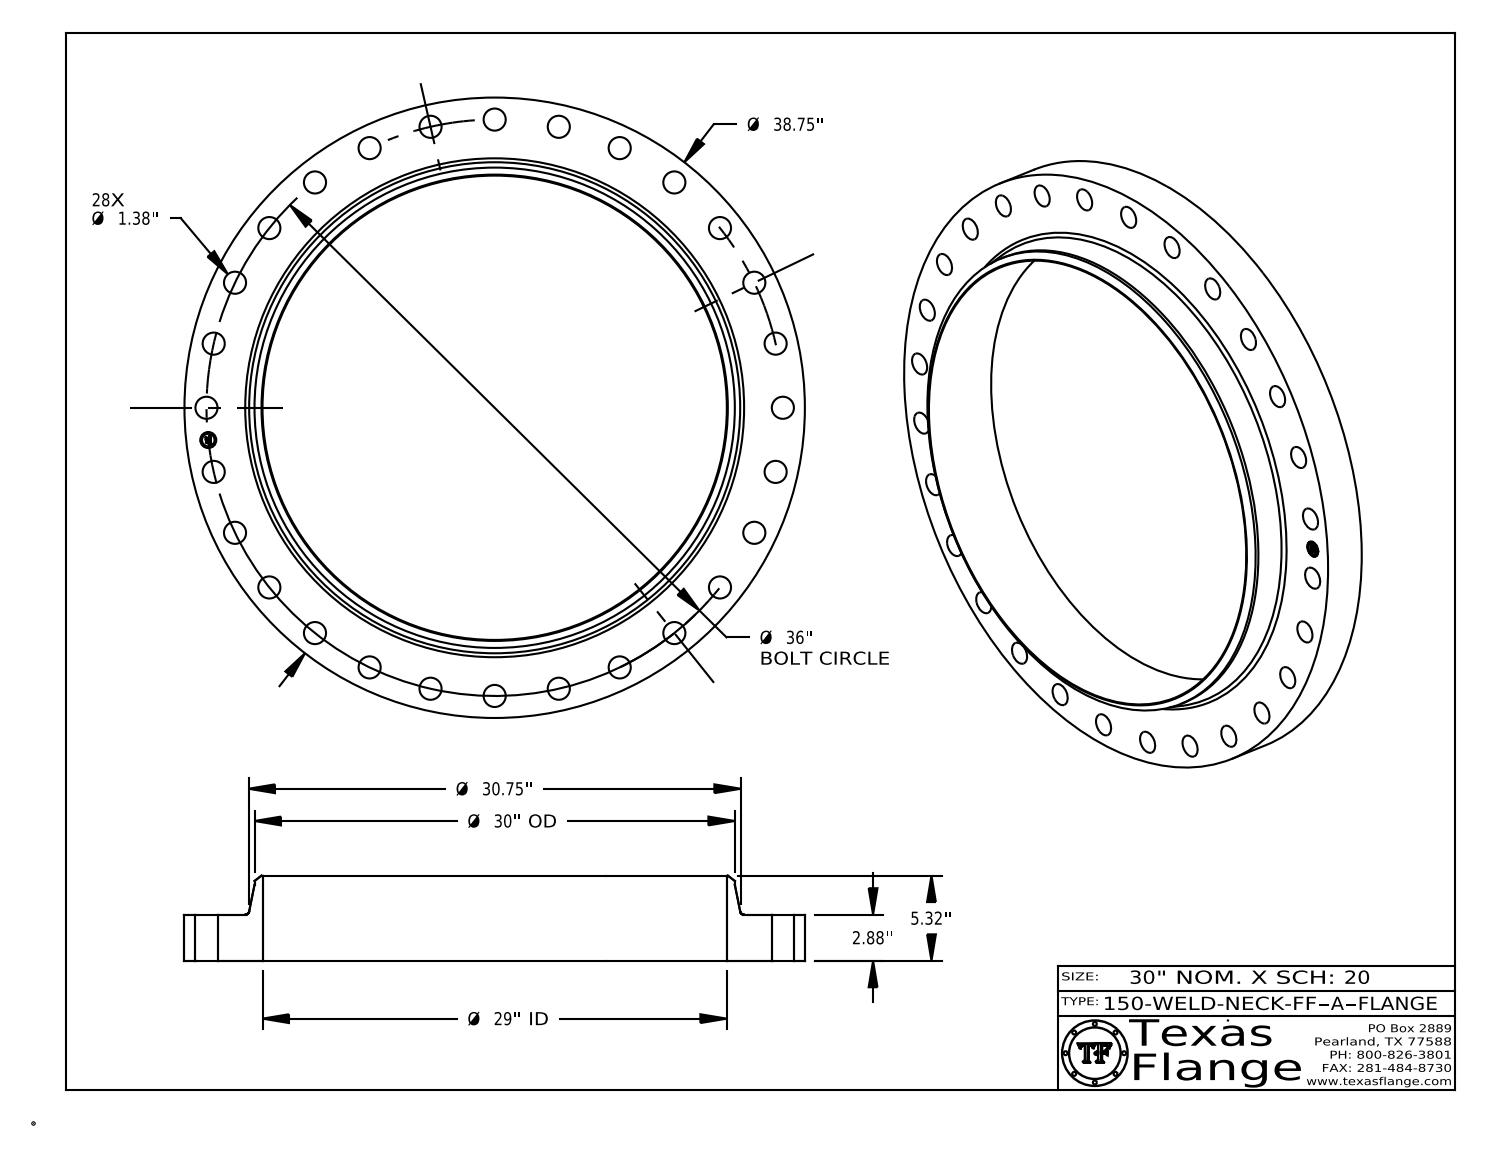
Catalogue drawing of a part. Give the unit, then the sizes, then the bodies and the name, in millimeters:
Units: millimetres
Overall size (bounding box): 984.3 × 984.3 × 135.1
Round holes (diameter × count): ⌀35.1 ×28, ⌀25.4 ×1, ⌀736.6 ×1
Round bosses / shafts (diameter × count): ⌀1.5 ×8, ⌀984.3 ×1, ⌀762 ×1, ⌀20 ×1
Main face-to-face distances: 73.2, 135.1, 62, 0.4, 72.8, 62.4, 7.6, 7.4, 1.4, 4.9
Hole centre spacings: 457.2, 486.5, 102.4, 203.5, 302, 396.7, 570.1, 646.6
Volume: 24 810 000 mm³ · Surface area: 1 491 000 mm²
Bodies: 1 solid, 456 faces (368 planar, 82 cylindrical, 6 other)
Part name (STEP PRODUCT): 150-WELD-NECK-FF, Series A
STEP written by: CATIA V5 STEP AP214 (AUTOMOTIVE_DESIGN)
